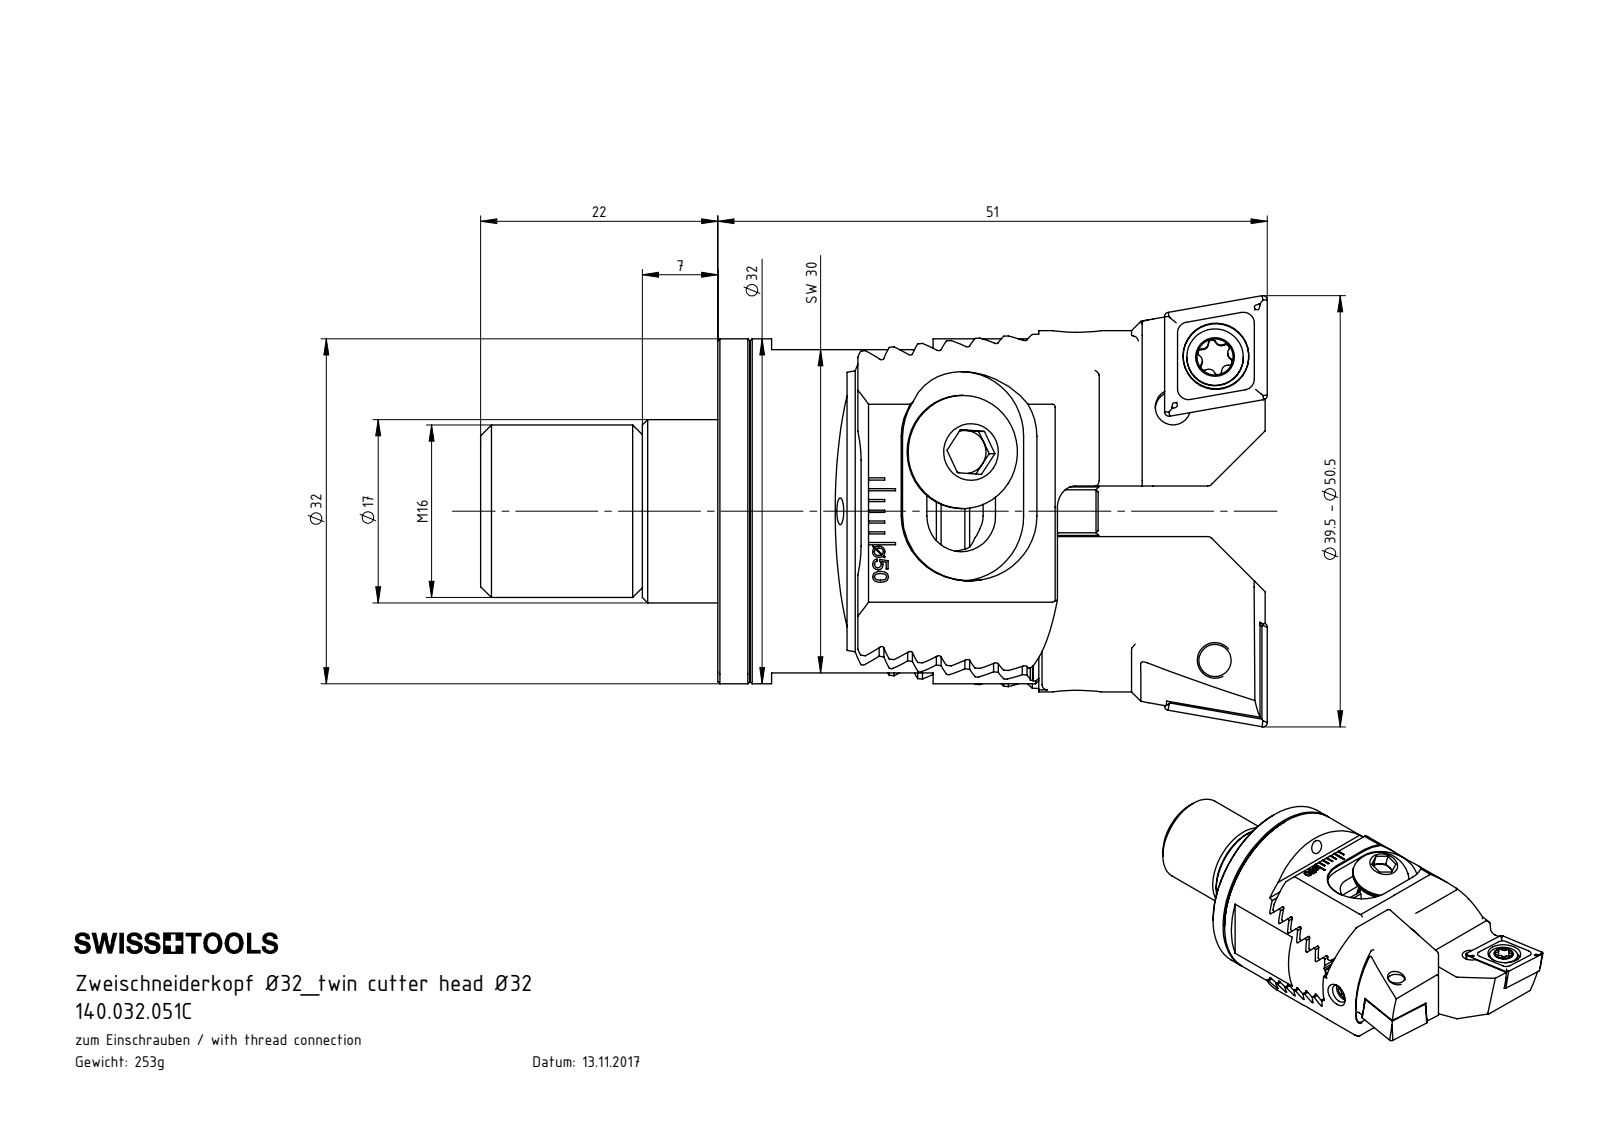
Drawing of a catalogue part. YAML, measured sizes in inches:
part_name: "Z32-ER1.002.016_A; HP5-Z32.040.051_A; WCB-ER2.001.009_A; Z32-WCB.001.021 (+8 more)"
step_written_by: "SolidWorks 2017 (CONFIG_CONTROL_DESIGN)"
units: inches
bodies: {solids: 16, faces: 985, planar: 457, cylindrical: 232, other: 296}
overall_size: [2.874, 1.575, 1.26]
volume: 1.965
surface_area: 30.38
round_holes:
  - {diameter: 0.098, count: 5}
  - {diameter: 0.13, count: 5}
  - {diameter: 0.063, count: 2}
  - {diameter: 0.079, count: 2}
  - {diameter: 0.173, count: 2}
  - {diameter: 0.197, count: 2}
  - {diameter: 0.24, count: 2}
  - {diameter: 0.252, count: 2}
  - {diameter: 0.268, count: 2}
  - {diameter: 0.138, count: 1}
  - {diameter: 0.402, count: 1}
  - {diameter: 0.492, count: 1}
round_bosses_or_shafts:
  - {diameter: 0.157, count: 4}
  - {diameter: 0.413, count: 2}
  - {diameter: 0.402, count: 2}
  - {diameter: 0.236, count: 2}
  - {diameter: 0.207, count: 2}
  - {diameter: 1.26, count: 1}
  - {diameter: 0.63, count: 1}
  - {diameter: 0.472, count: 1}
partial_cylinders:
  - {radius: 0.02, count: 16}
  - {radius: 0.008, count: 14}
  - {radius: 0.008, count: 12}
  - {radius: 0.013, count: 12}
  - {radius: 0.023, count: 12}
  - {radius: 0.079, count: 4}
  - {radius: 0.13, count: 4}
  - {radius: 0.236, count: 4}
face_to_face_distances: [0.094, 0.187, 0.281, 0.118, 0.375, 0.375, 0.193, 0.469, 0.281, 0.096]
hole_center_spacings: [0.239, 0.244, 0.954, 0.958, 1.128, 0.354, 0.355, 0.685]
